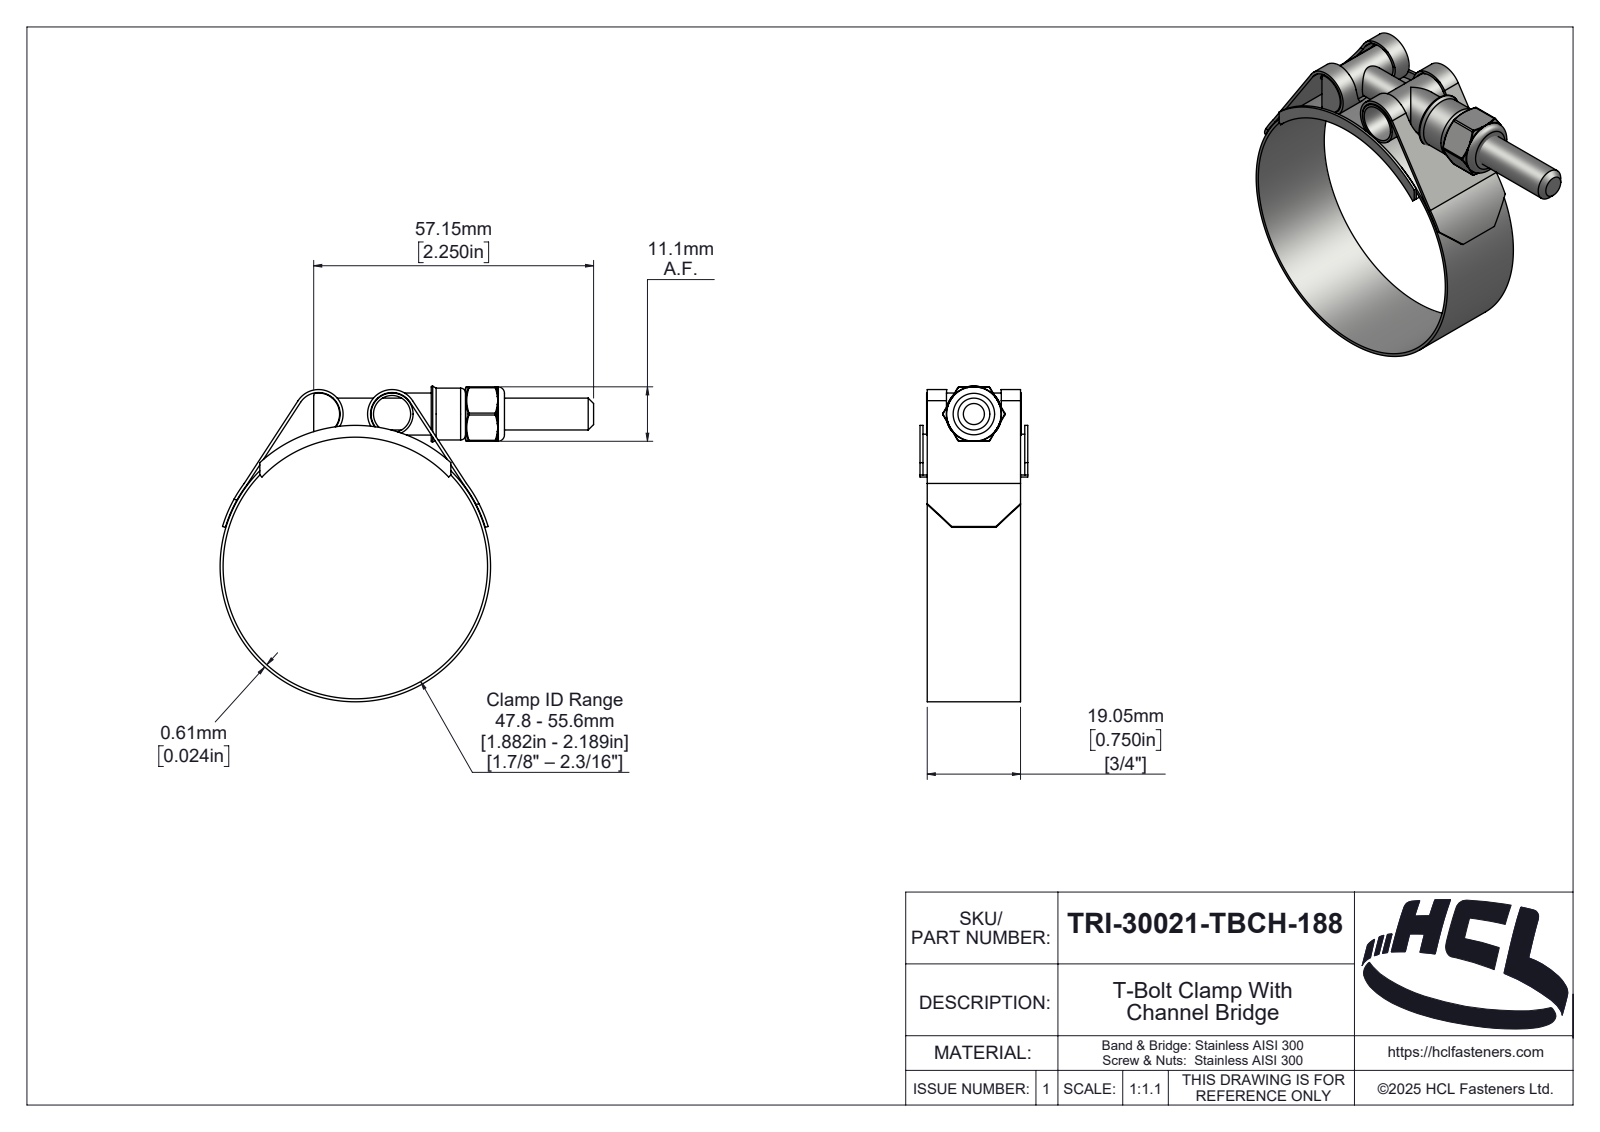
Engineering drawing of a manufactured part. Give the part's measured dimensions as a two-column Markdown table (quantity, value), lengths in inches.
| quantity | value |
| --- | --- |
| part name | TRI-30021-TBCH-188 |
| STEP written by | SolidWorks 2025 (AUTOMOTIVE_DESIGN) |
| units | inches |
| bodies | 6 solids, 338 faces (50 planar, 126 cylindrical, 162 other) |
| overall size | 3.002 × 2.537 × 0.866 |
| volume | 0.43 in³ |
| surface area | 23.77 in² |
| round holes (diameter × count) | 0.213 × 1, 0.25 × 1, 0.256 × 1, 0.298 × 1, 2.126 × 1 |
| round bosses / shafts (diameter × count) | 0.338 × 2, 2.174 × 1, 0.417 × 1 |
| partial cylindrical surfaces (radius × count) | 0.015 × 6, 0.02 × 2, 0.173 × 2, 0.197 × 2, 0.22 × 2, 0.023 × 1, 0.095 × 1, 0.119 × 1 |
| main face-to-face distances | 0.024, 0.058, 0.808, 0.029, 0.842, 0.034, 0.784, 0.75, 0.437, 0.866 |
| hole center spacings | 1.26 |
